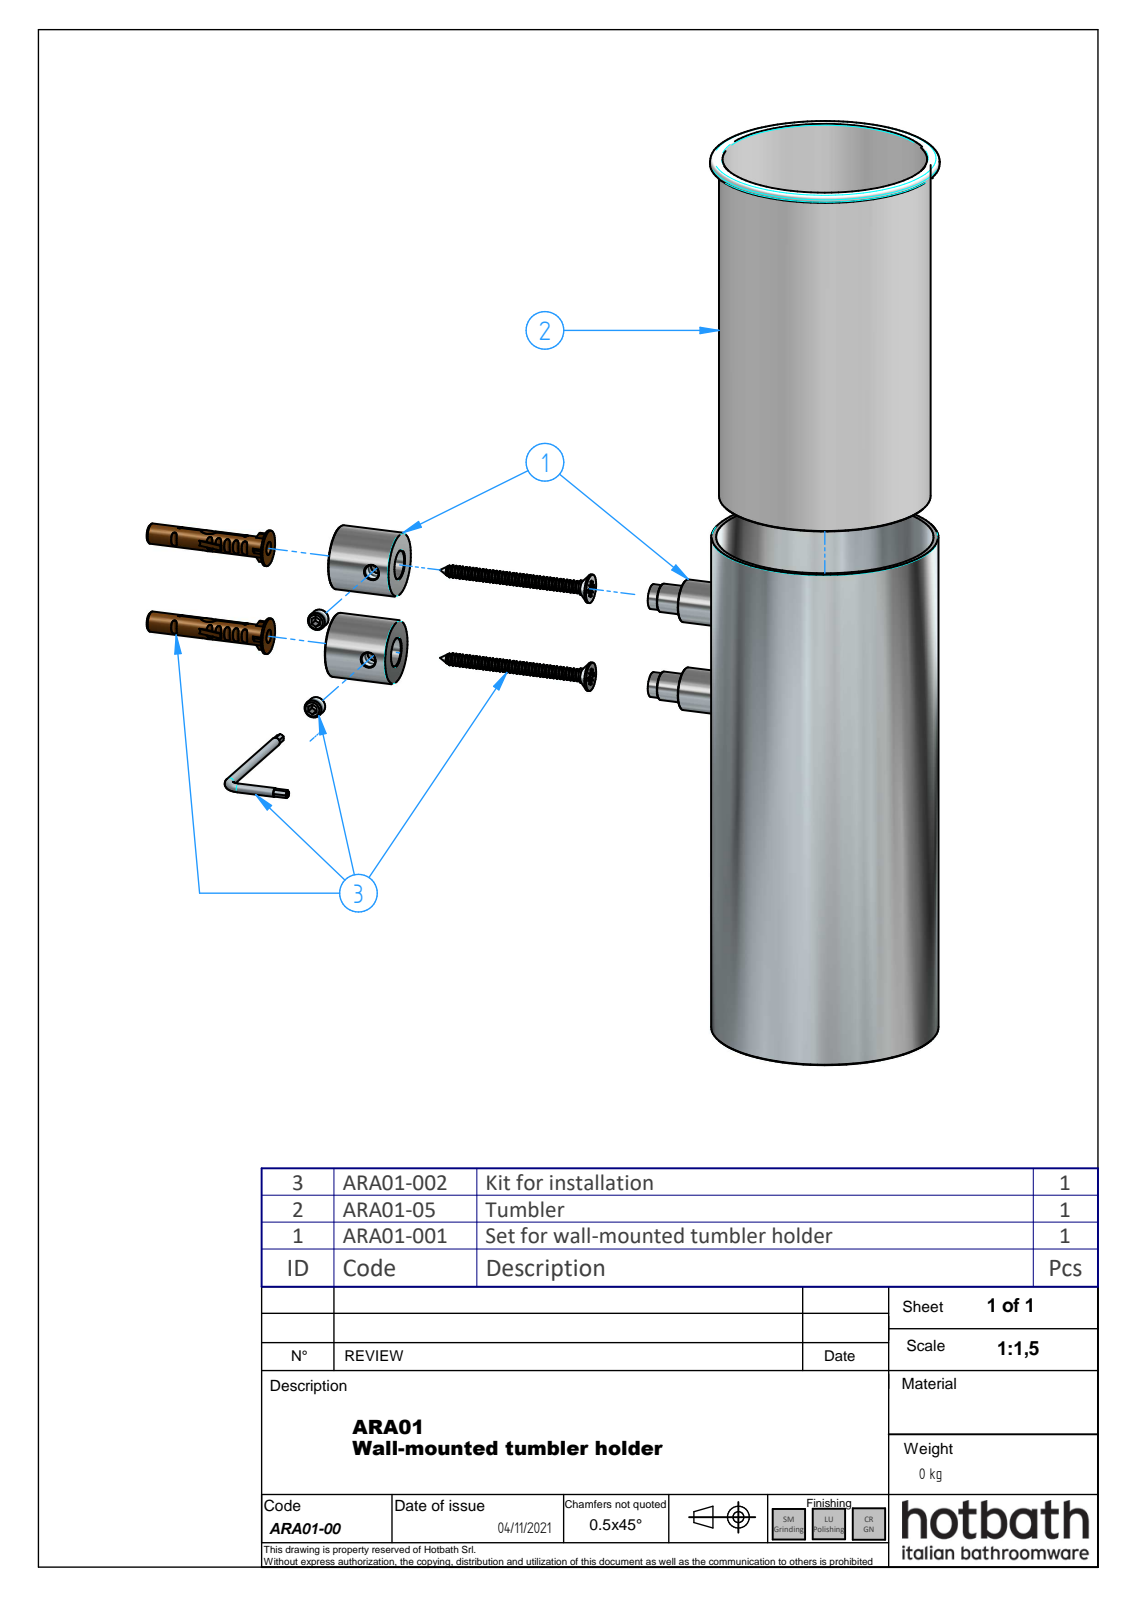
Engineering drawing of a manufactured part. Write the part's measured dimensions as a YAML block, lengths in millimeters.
part_name: "ARA01-00; ARA01-05; ARA01-001; ARA01-01 (+7 more)"
step_written_by: "ST-DEVELOPER v16.7 (AP242_MANAGED_MODEL_BASED_3D_ENGINEERING_MIM_LF)"
units: millimeters
bodies: {solids: 13, faces: 264, planar: 128, cylindrical: 75, other: 61}
overall_size: [147, 127.13, 64]
volume: 94629
surface_area: 116186
round_holes:
  - {diameter: 1, count: 2}
  - {diameter: 1.7, count: 2}
  - {diameter: 2, count: 2}
  - {diameter: 3.24, count: 2}
  - {diameter: 3.7, count: 2}
  - {diameter: 4.13, count: 2}
  - {diameter: 4.2, count: 2}
  - {diameter: 4.92, count: 2}
  - {diameter: 8, count: 2}
  - {diameter: 30, count: 1}
  - {diameter: 57, count: 1}
  - {diameter: 60.6, count: 1}
round_bosses_or_shafts:
  - {diameter: 18, count: 2}
  - {diameter: 12, count: 2}
  - {diameter: 10, count: 2}
  - {diameter: 7, count: 2}
  - {diameter: 5.7, count: 2}
  - {diameter: 5, count: 2}
  - {diameter: 4, count: 2}
  - {diameter: 64, count: 1}
partial_cylinders:
  - {radius: 0.8, count: 12}
face_to_face_distances: [1, 47, 48, 10, 37, 38, 145, 135, 98, 97]
hole_center_spacings: [26, 19.5, 66.63, 86.13]
